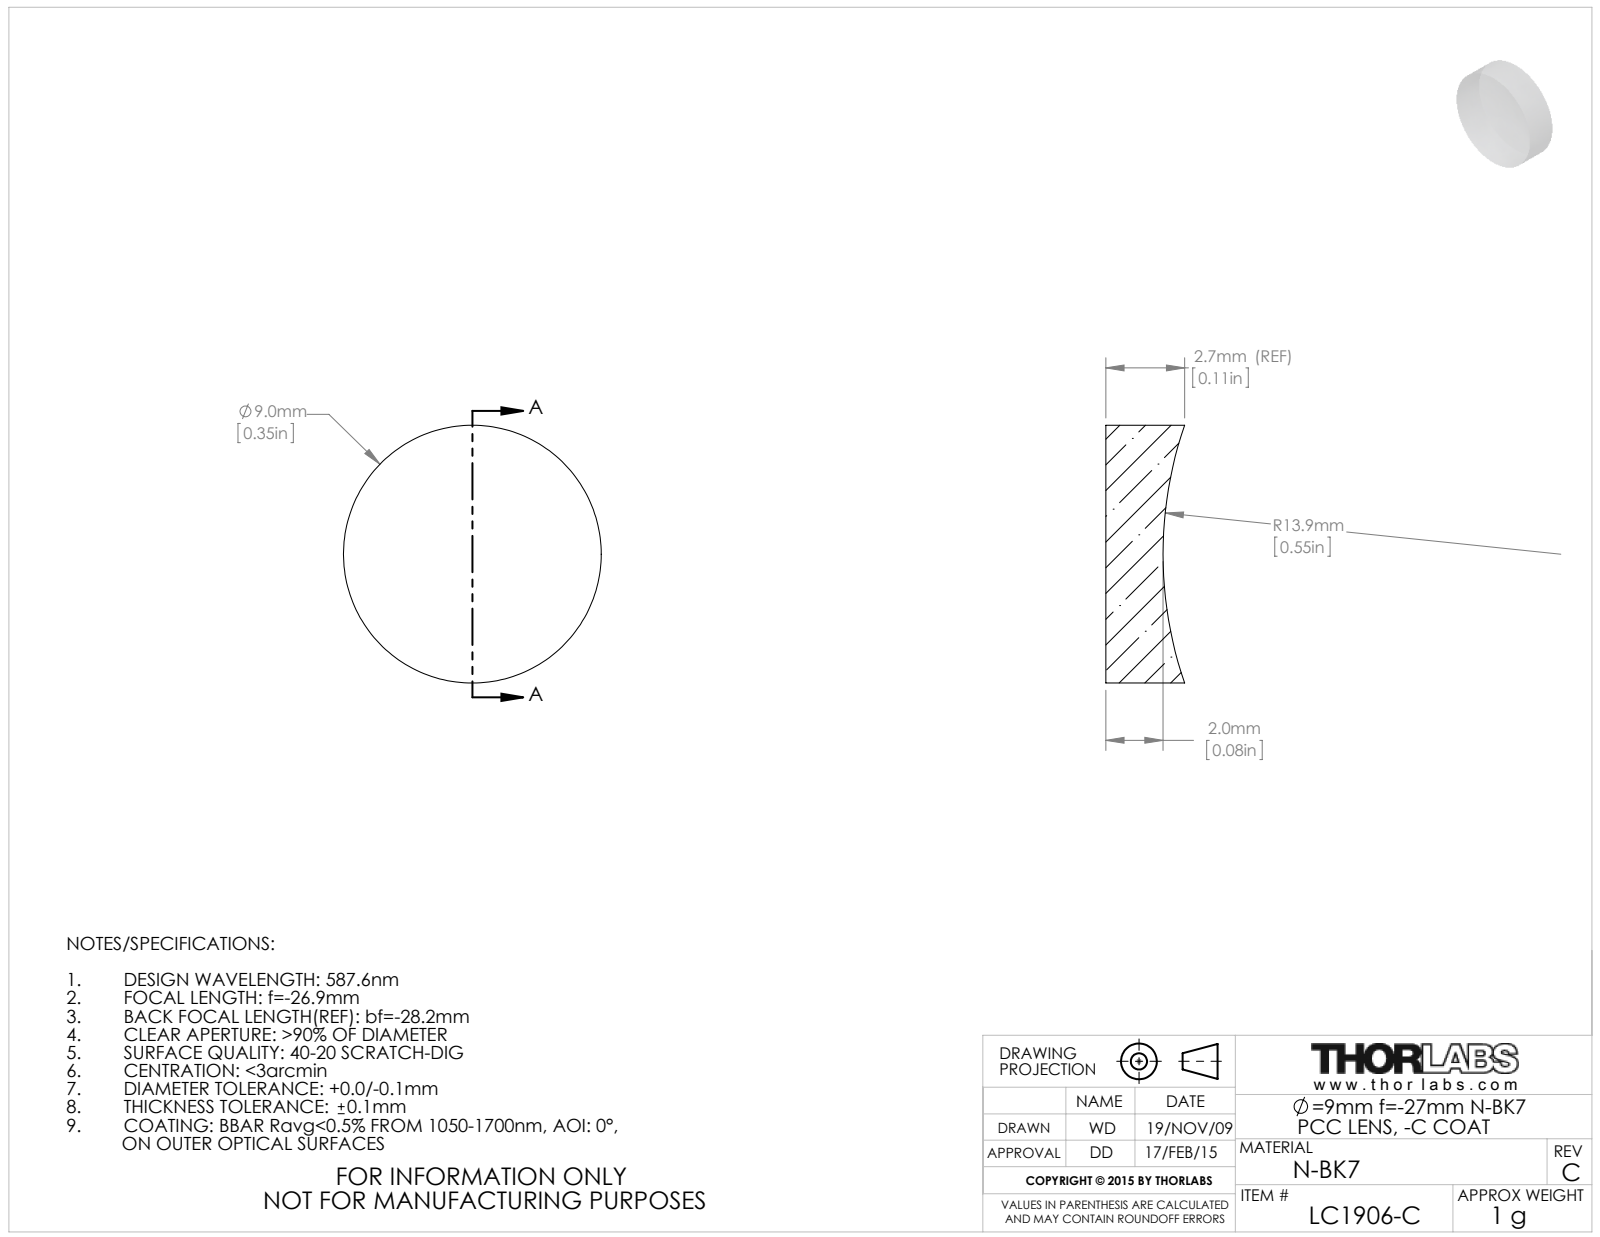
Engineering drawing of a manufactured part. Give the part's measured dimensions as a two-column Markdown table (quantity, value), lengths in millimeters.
| quantity | value |
| --- | --- |
| part name | 4800-E0W |
| STEP written by | SolidWorks 2009 (AUTOMOTIVE_DESIGN) |
| units | millimeters |
| bodies | 1 solid, 5 faces (1 planar, 2 cylindrical, 2 other) |
| overall size | 9 × 9 × 2.75 |
| volume | 151 mm³ |
| surface area | 207 mm² |
| round bosses / shafts (diameter × count) | 9 × 1 |
